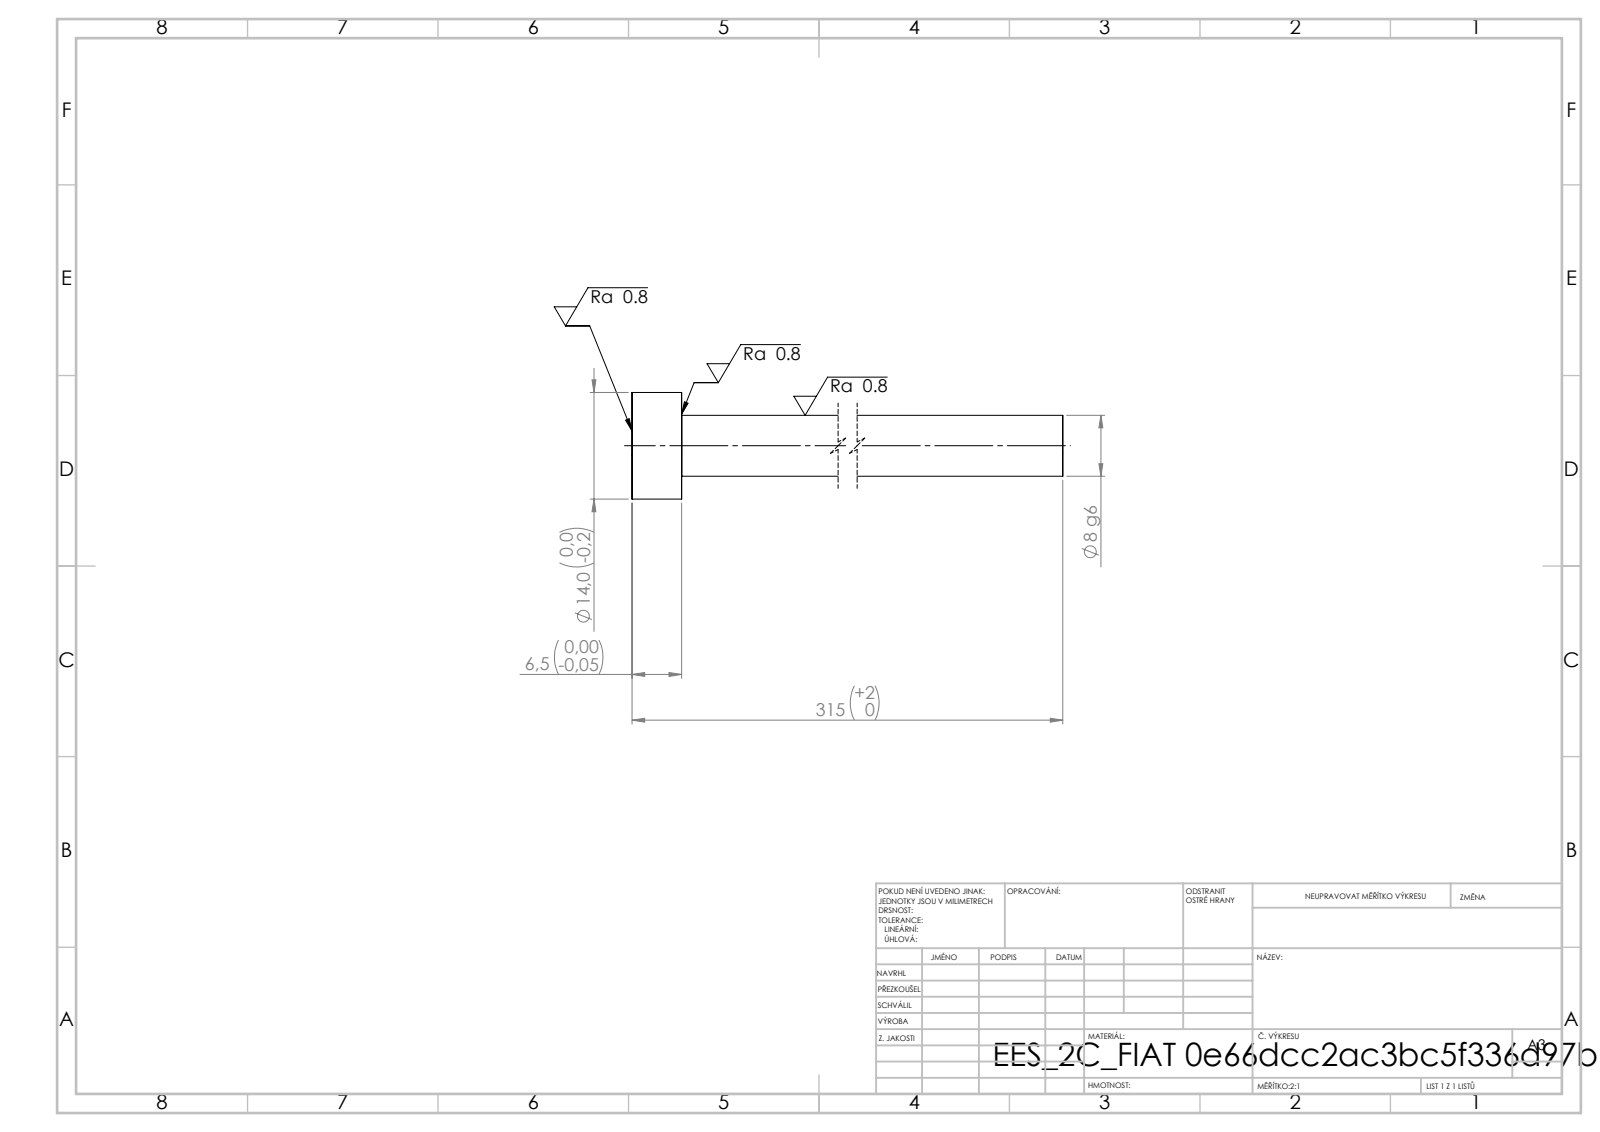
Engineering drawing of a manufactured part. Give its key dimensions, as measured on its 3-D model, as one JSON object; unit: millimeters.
{"step_written_by": "SolidWorks 2019 (CONFIG_CONTROL_DESIGN)", "units": "millimeters", "bodies": {"solids": 1, "faces": 7, "planar": 3, "cylindrical": 4, "other": 0}, "overall_size": [315, 14, 14], "volume_mm3": 16507, "surface_area_mm2": 8347, "round_bosses_or_shafts": [[14, 1], [8, 1]], "face_to_face_distances": [6.5, 315, 308.5]}
